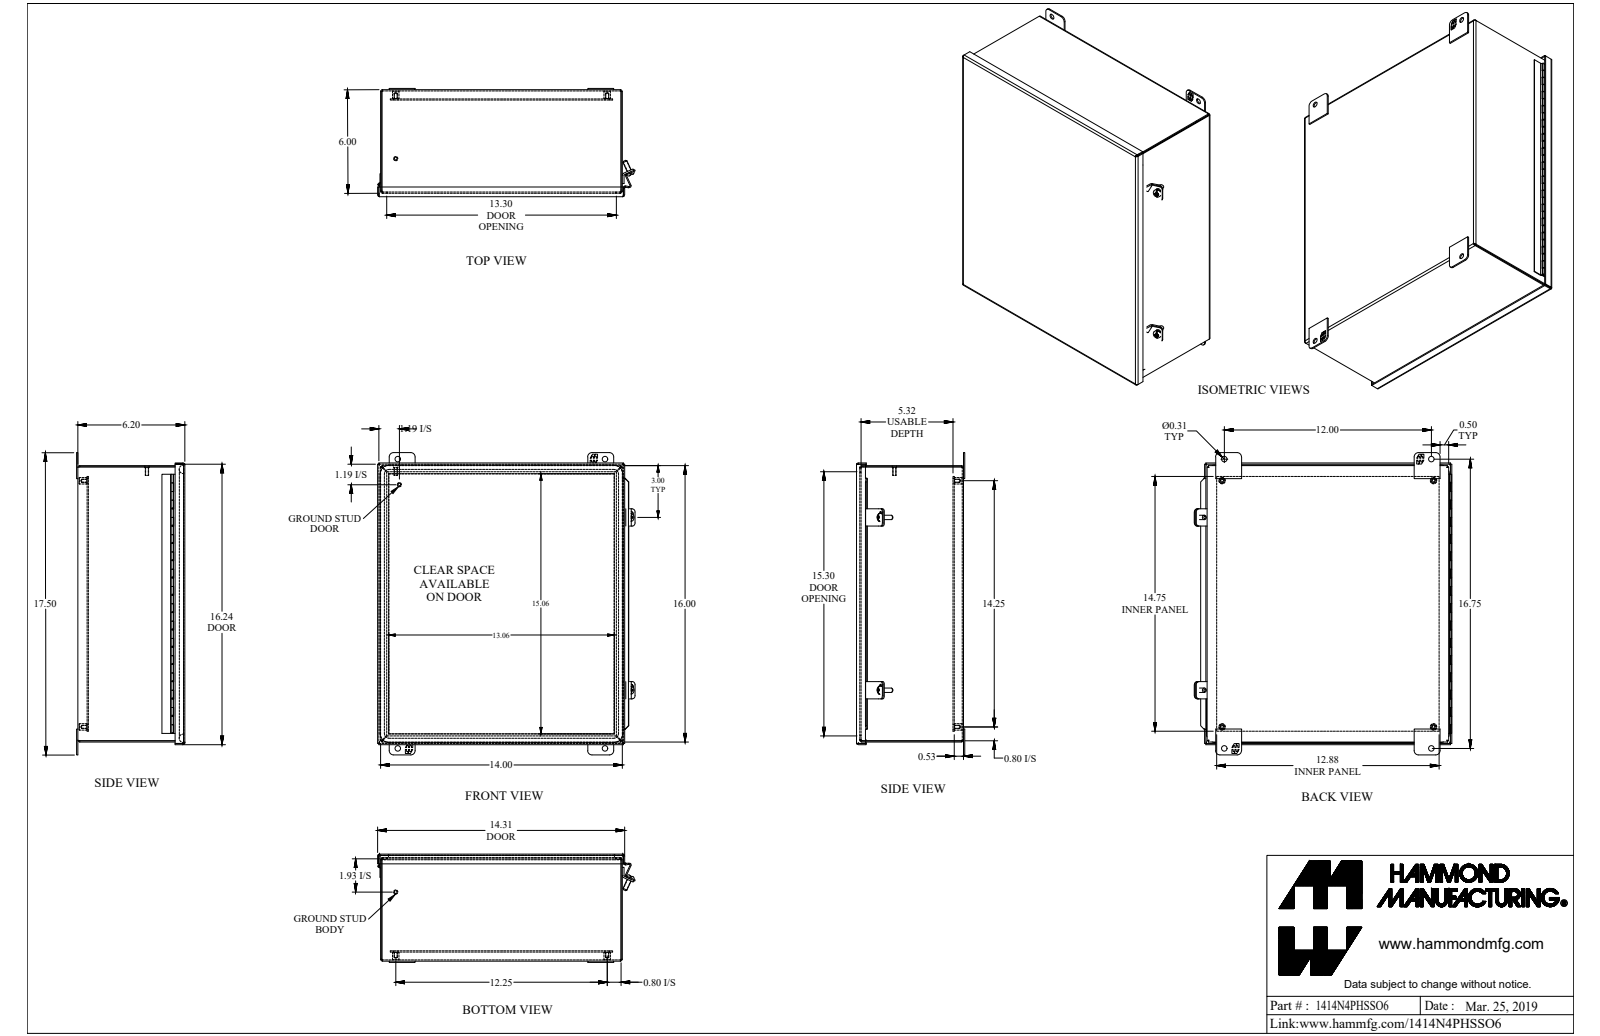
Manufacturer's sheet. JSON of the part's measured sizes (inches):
{"part_name": "1414N4PHSSO6", "step_written_by": "SolidWorks 2018 (AUTOMOTIVE_DESIGN)", "units": "inches", "bodies": {"solids": 21, "faces": 780, "planar": 496, "cylindrical": 220, "other": 64}, "overall_size": [17.5, 14.903, 6.269], "volume_in3": 82.81, "surface_area_in2": 2319, "round_holes": [[0.156, 4], [0.265, 4], [0.313, 4], [0.213, 2], [0.05, 1]], "round_bosses_or_shafts": [[0.375, 4], [0.25, 4], [0.48, 2], [0.19, 2], [0.1, 1], [0.045, 1]], "partial_cylinders_radius": [[0.25, 24], [0.036, 9], [0.108, 9], [0.188, 8], [0.007, 4], [0.046, 4], [0.079, 4], [0.118, 4]], "face_to_face_distances": [0.072, 6.125, 5.593, 0.532, 6.197, 6.053, 0.604, 5.665, 0.46, 5.521], "hole_center_spacings": [12.189, 19.679, 1.256, 1.257, 12.25, 12.25, 14.25, 14.25]}
